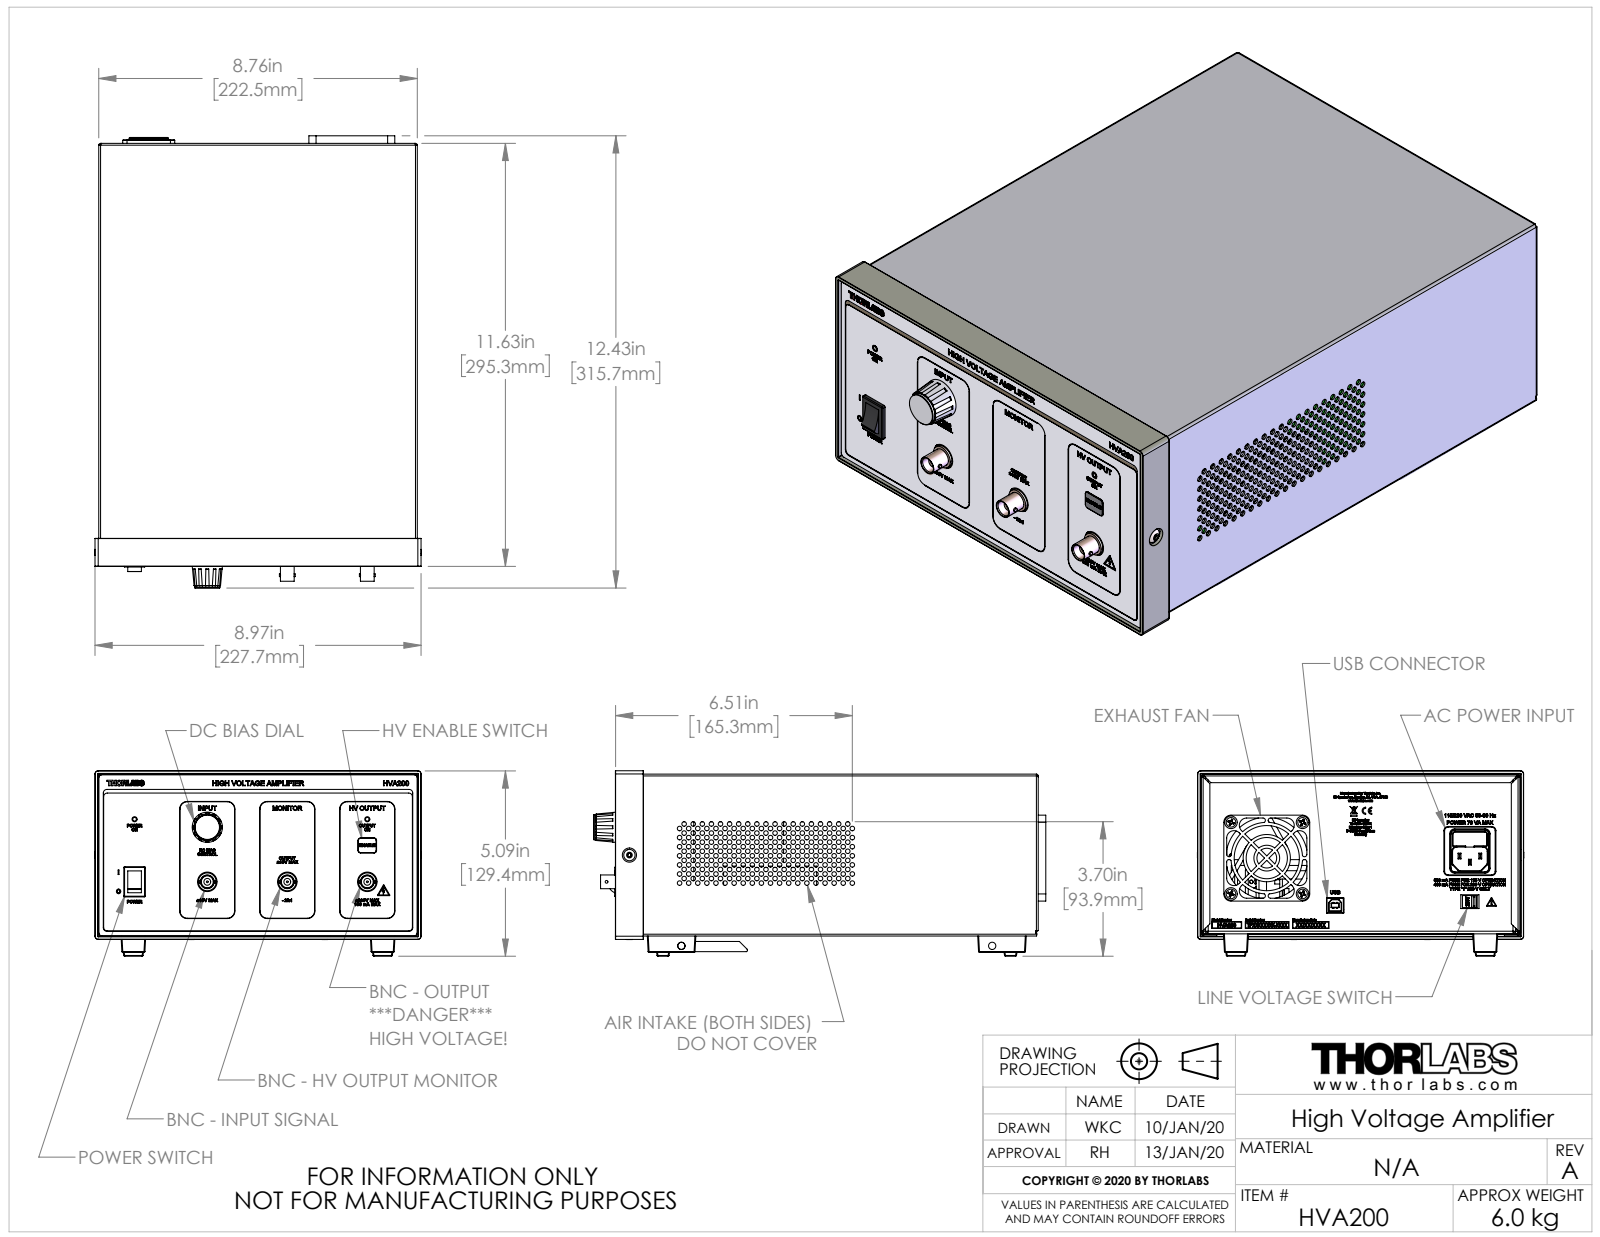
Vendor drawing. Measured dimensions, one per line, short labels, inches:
name: HVA200_WKC
written by: SolidWorks 2018 (AUTOMOTIVE_DESIGN)
unit: in
bodies: 56 solids, 9635 faces (5111 planar, 1517 cylindrical, 3007 other)
size: 12.431 × 8.974 × 5.098
volume: 69.49 in³; area: 1 605 in²
holes: 219× ⌀0.125, 69× ⌀0.125, 13× ⌀0.213, 12× ⌀0.188, 6× ⌀0.12, 6× ⌀0.16, 5× ⌀0.096, 5× ⌀0.163, 5× ⌀0.166, 4× ⌀0.126, 4× ⌀0.138, 4× ⌀0.162
bosses: 144× ⌀0.116, 13× ⌀0.164, 10× ⌀0.201, 8× ⌀0.12, 4× ⌀0.138, 3× ⌀0.49, 3× ⌀0.43, 3× ⌀0.378
rounds: 52× R0.025, 37× R0.02, 32× R0.005, 29× R0.1, 22× R0.01, 14× R0.118, 13× R0.039, 12× R0.2
face distances: 0.063, 0.04, 0.5, 4.39, 4.328, 4.35, 4.288, 8.72, 0.072, 0.112
hole spacings: 0.25, 0.5, 0.75, 1, 1.25, 1.5, 1.75, 2.5
